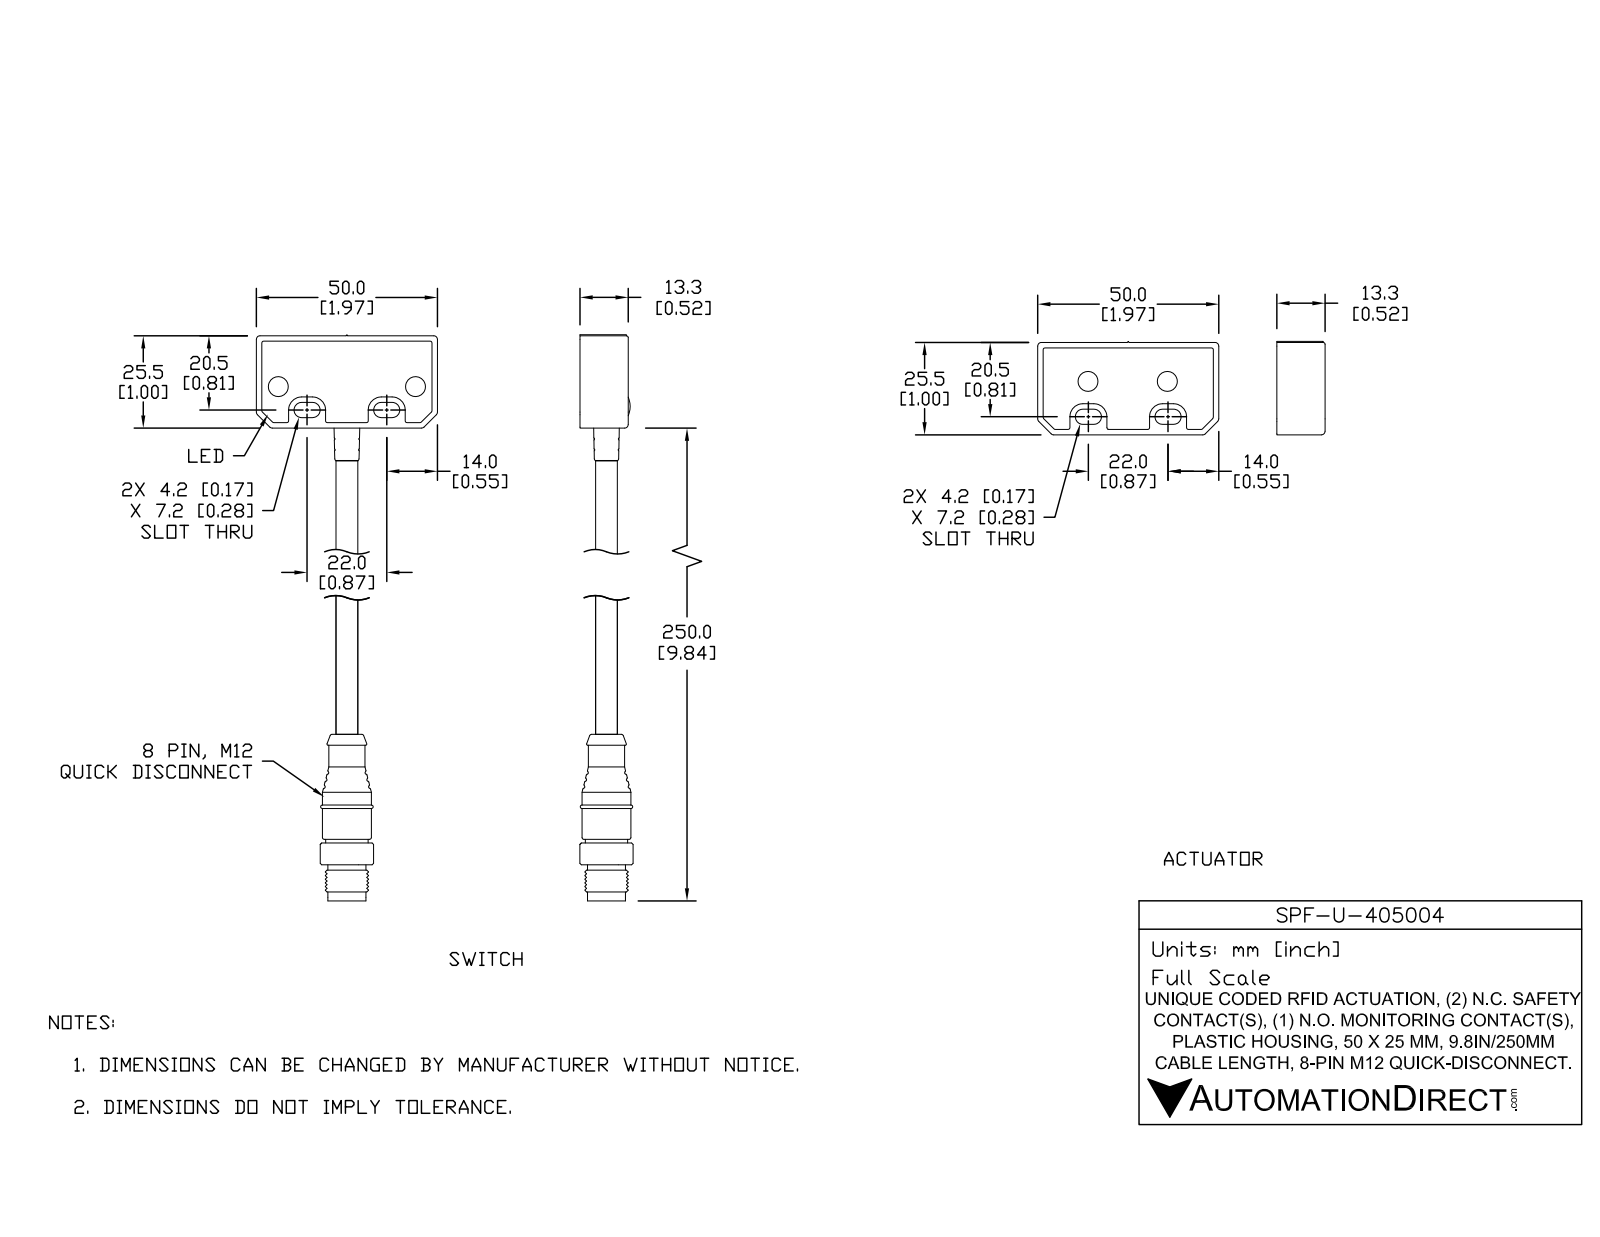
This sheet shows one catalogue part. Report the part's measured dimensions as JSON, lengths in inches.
{"part_name": "SPF-U-405004; SPF-U-405004_2; SPF-U-405004_1", "step_written_by": "SolidWorks 2017 (AUTOMOTIVE_DESIGN)", "units": "inches", "bodies": {"solids": 13, "faces": 1506, "planar": 632, "cylindrical": 472, "other": 402}, "overall_size": [11.89, 1.969, 0.579], "volume_in3": 1.486, "surface_area_in2": 43.7, "round_holes": [[0.197, 4], [0.119, 1], [0.173, 1], [0.213, 1], [0.232, 1], [0.276, 1], [0.327, 1], [0.465, 1]], "round_bosses_or_shafts": [[0.031, 10], [0.079, 4], [0.193, 2], [0.531, 1], [0.461, 1], [0.413, 1], [0.394, 1], [0.374, 1]], "partial_cylinders_radius": [[0.02, 132], [0.039, 36], [0.079, 8], [0.083, 8], [0.142, 8], [0.181, 8], [0.012, 6], [0.14, 4]], "face_to_face_distances": [0.059, 0.457, 0.398, 0.047, 0.445, 0.504, 1.043, 0.098, 0.945, 1.909], "hole_center_spacings": [0.221, 0.862, 1.062, 1.065, 1.283, 1.492, 1.55, 1.559]}
